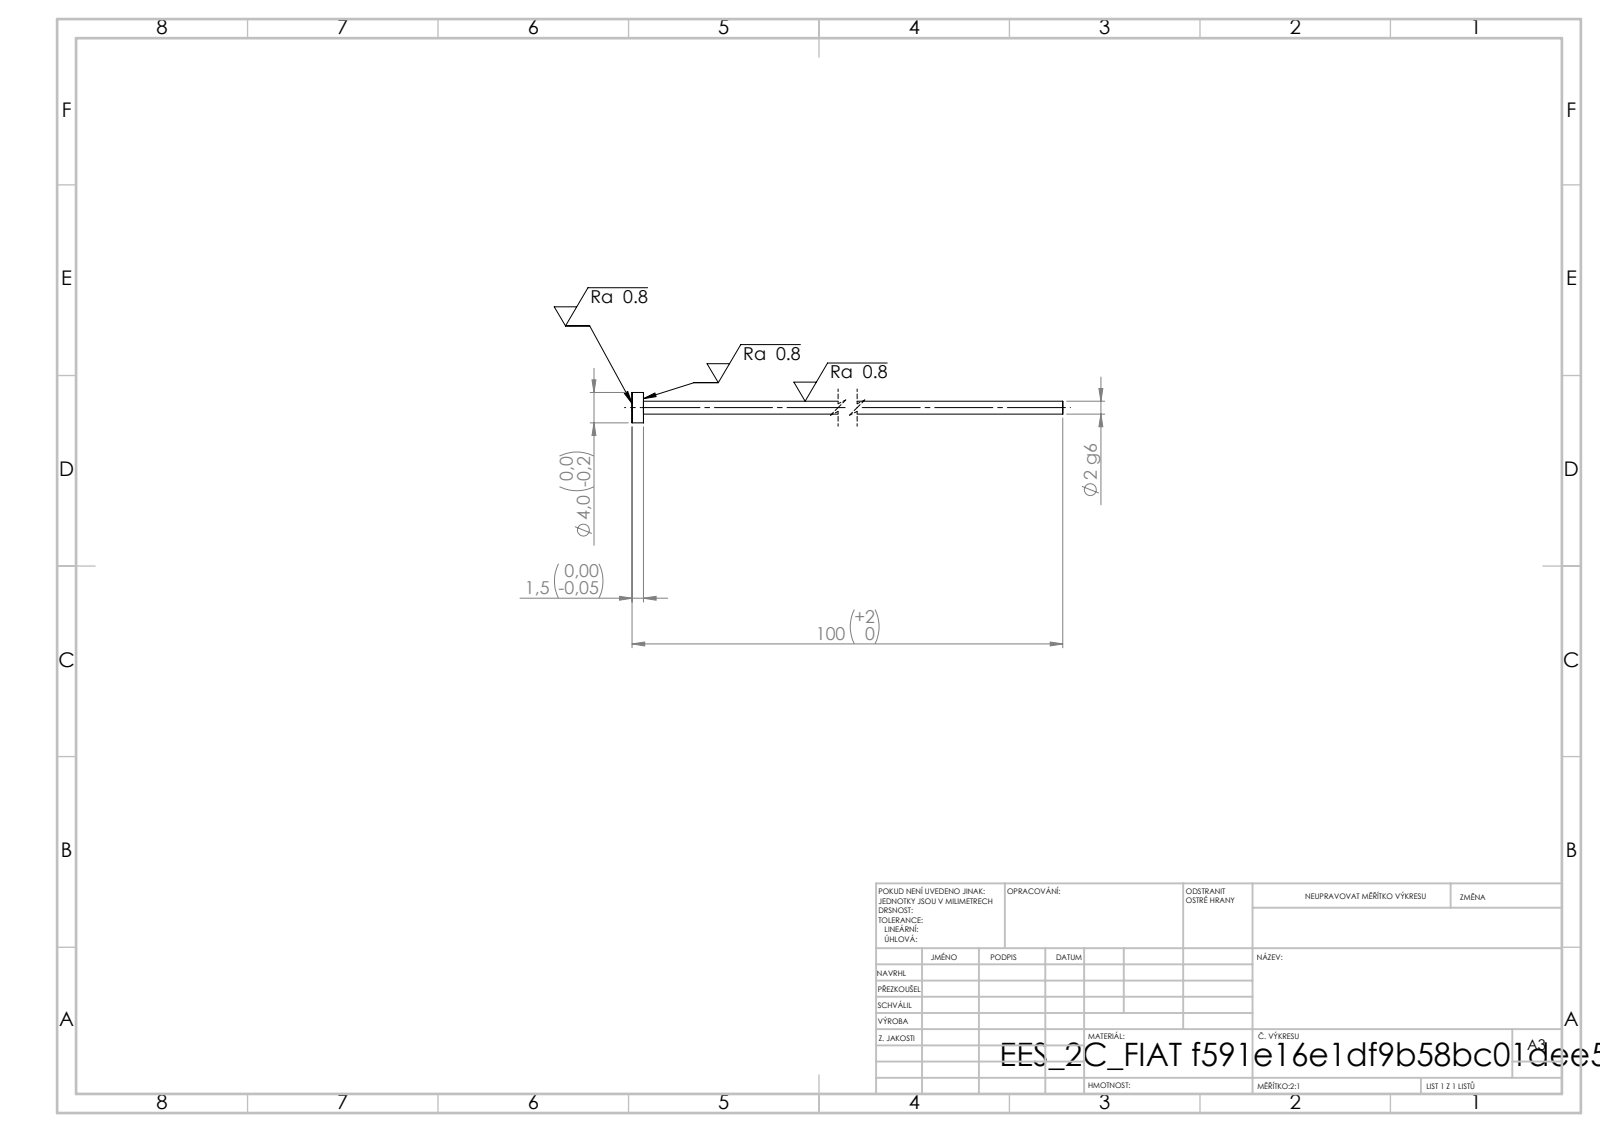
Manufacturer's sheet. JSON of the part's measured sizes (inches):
{"step_written_by": "SolidWorks 2019 (CONFIG_CONTROL_DESIGN)", "units": "inches", "bodies": {"solids": 1, "faces": 7, "planar": 3, "cylindrical": 4, "other": 0}, "overall_size": [3.937, 0.157, 0.157], "volume_in3": 0.015, "surface_area_in2": 0.884, "round_bosses_or_shafts": [[0.157, 1], [0.067, 1]], "face_to_face_distances": [0.059, 3.937, 3.878]}
